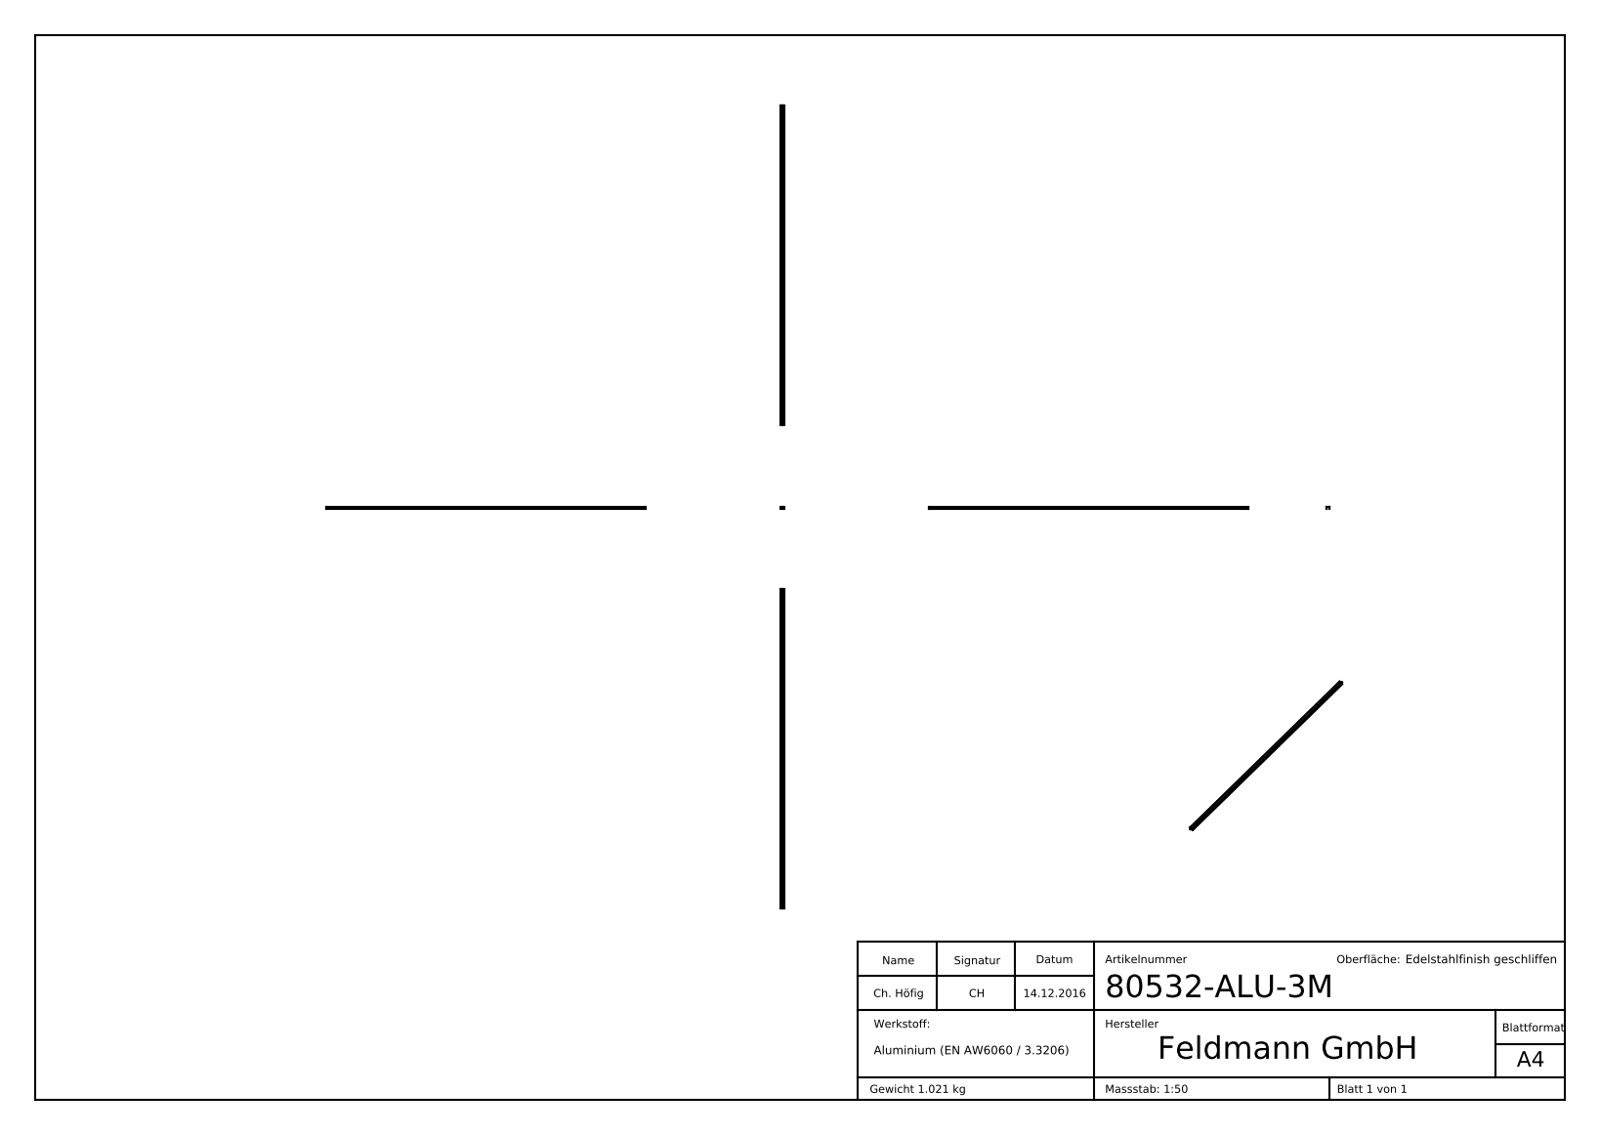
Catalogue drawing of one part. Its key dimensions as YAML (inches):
part_name: "80532-ALU-3M"
step_written_by: "SolidWorks 2015 (CONFIG_CONTROL_DESIGN)"
units: inches
bodies: {solids: 1, faces: 283, planar: 151, cylindrical: 6, other: 126}
overall_size: [118.11, 1.102, 0.787]
volume: 23.08
surface_area: 602.2
partial_cylinders:
  - {radius: 0.02, count: 4}
  - {radius: 0.079, count: 2}
face_to_face_distances: [0.079, 1.024, 1.102, 0.945, 0.709, 0.787, 118.11, 0.075, 0.949, 1.028]
